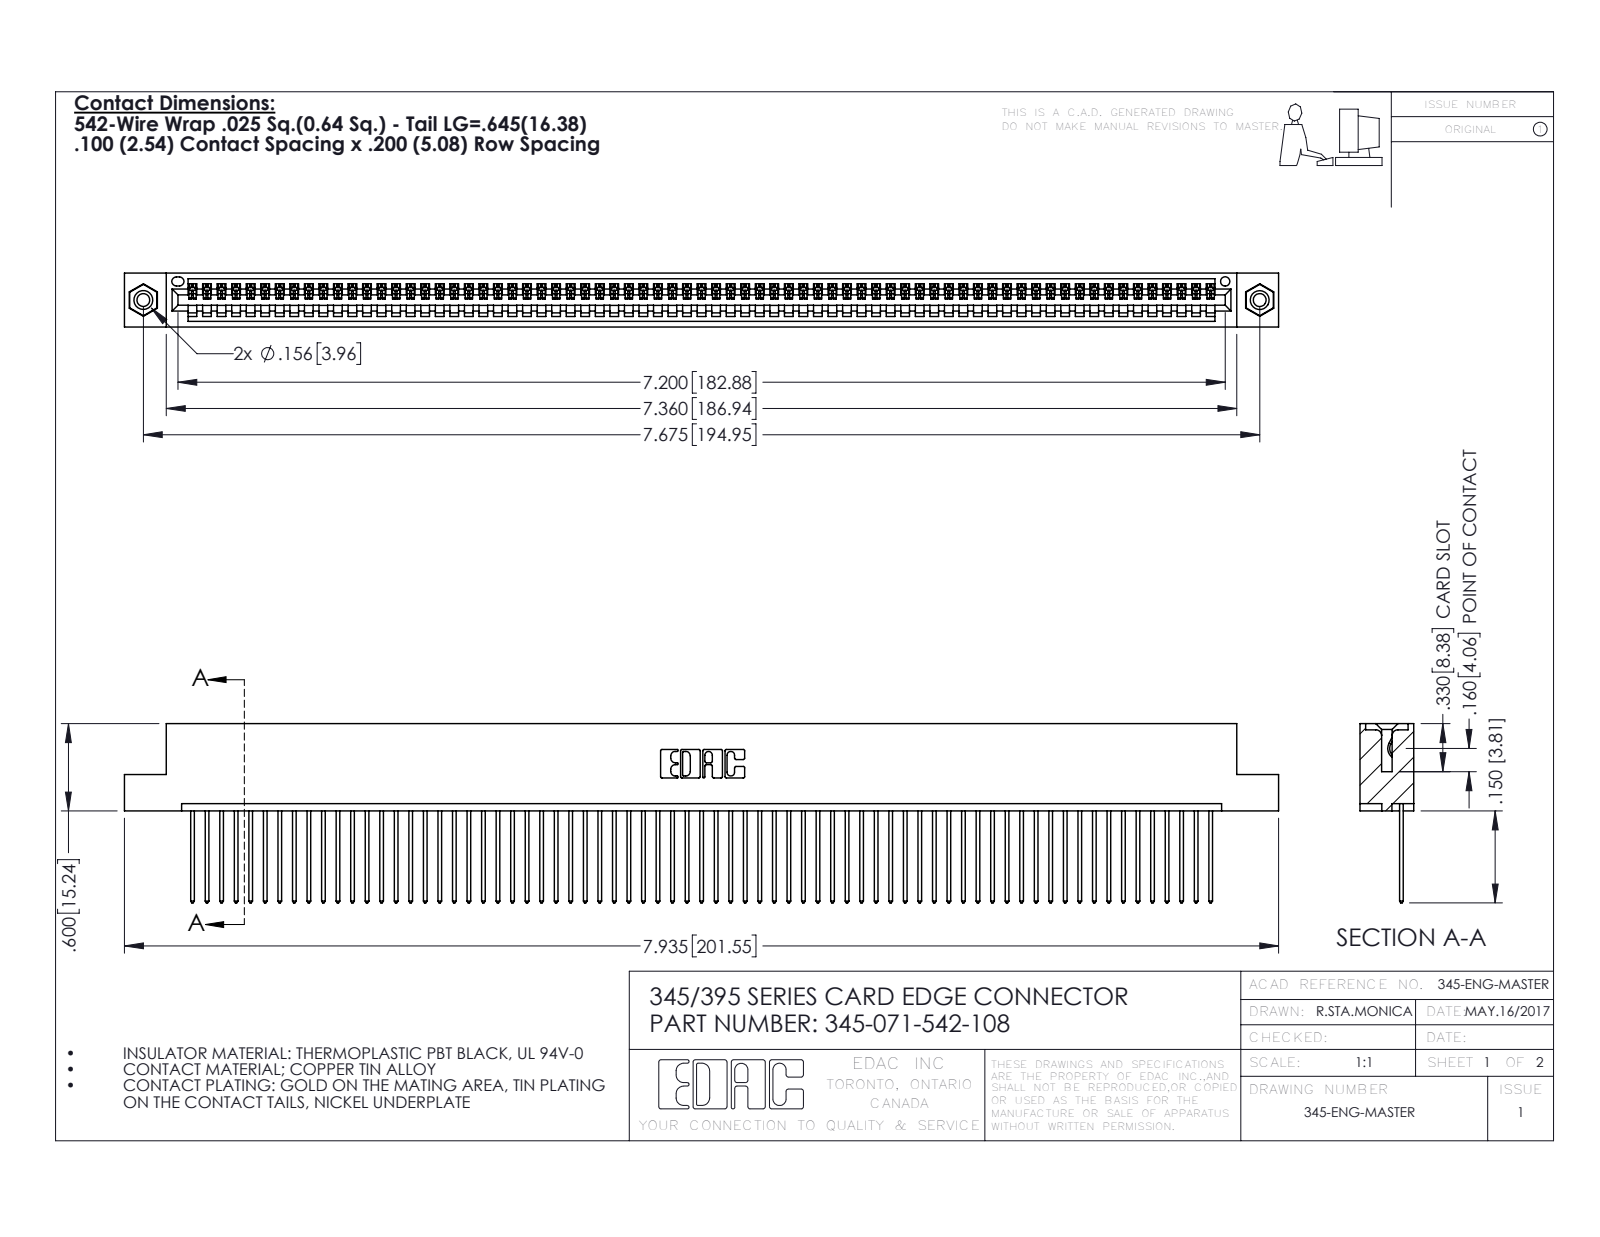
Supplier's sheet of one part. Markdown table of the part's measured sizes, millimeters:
| quantity | value |
| --- | --- |
| part name | 345-250-001_345-250-003-102; 345-292-001_345-293-142; 345 Part_Flush Mounting Lugs - 0.156 Dia-TI; 345-071-542-108 |
| STEP written by | SolidWorks 2016 (CONFIG_CONTROL_DESIGN) |
| units | millimeters |
| bodies | 74 solids, 4304 faces (2952 planar, 1336 cylindrical, 16 other) |
| overall size | 201.5 × 31.3 × 9.4 |
| volume | 19 530 mm³ |
| surface area | 27 370 mm² |
| round holes (diameter × count) | 2.3 × 2, 3.2 × 2, 4 × 2, 1.6 × 1 |
| round bosses / shafts (diameter × count) | 3.9 × 2 |
| partial cylindrical surfaces (radius × count) | 0.2 × 142, 0.3 × 142, 0.3 × 22, 0.2 × 6, 0.8 × 6, 0.7 × 3, 0.8 × 2, 1 × 2 |
| main face-to-face distances | 1.8, 7.6, 2.5, 6.9, 0.6, 9.4, 5.1, 5.7, 3.8, 1.8 |
| hole center spacings | 6.9, 189, 194.9 |
